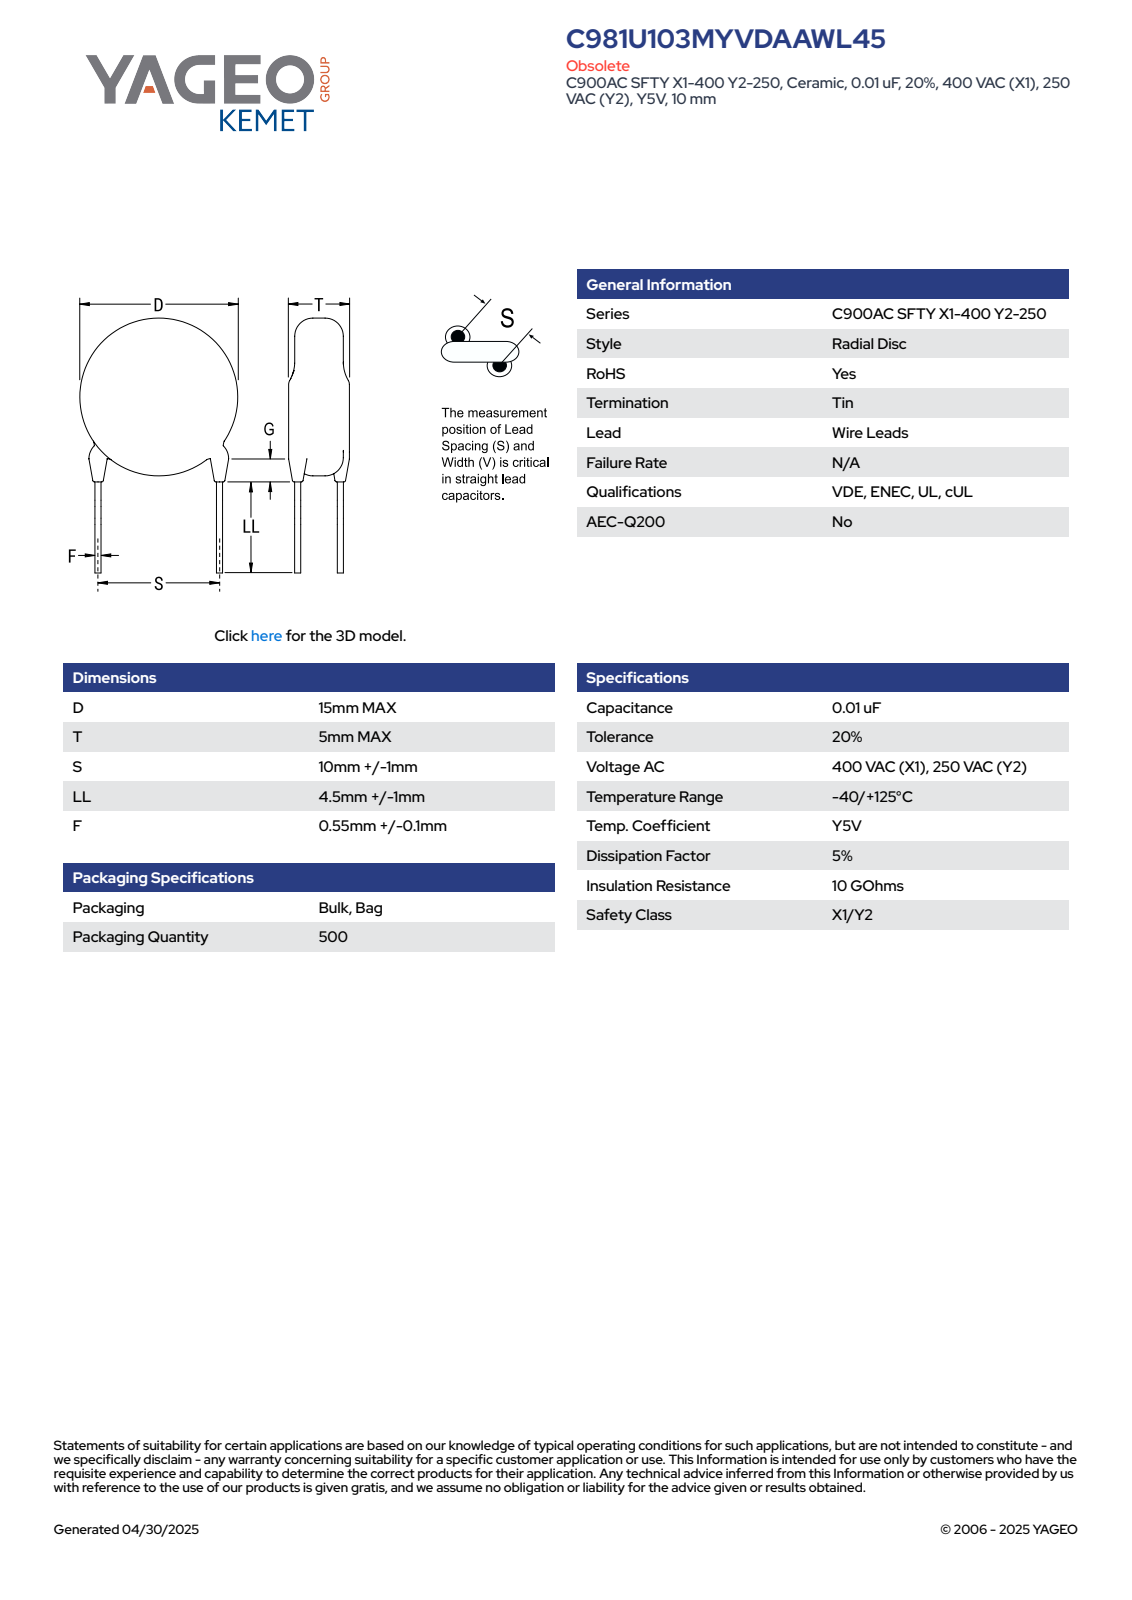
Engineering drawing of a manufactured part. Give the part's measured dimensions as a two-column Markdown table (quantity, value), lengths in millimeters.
| quantity | value |
| --- | --- |
| part name | CCD_STC900_D15T5S10LL5.5F0.65G3 |
| STEP written by | SolidWorks 2014 (AUTOMOTIVE_DESIGN) |
| units | millimeters |
| bodies | 4 solids, 83 faces (61 planar, 6 cylindrical, 16 other) |
| overall size | 20.78 × 15 × 5 |
| volume | 870 mm³ |
| surface area | 597 mm² |
| round bosses / shafts (diameter × count) | 0.65 × 2, 15 × 1 |
| main face-to-face distances | 5, 14.14, 12.41, 1.73, 0.33, 1.4, 0.32, 5.13, 5.33, 12.74 |
